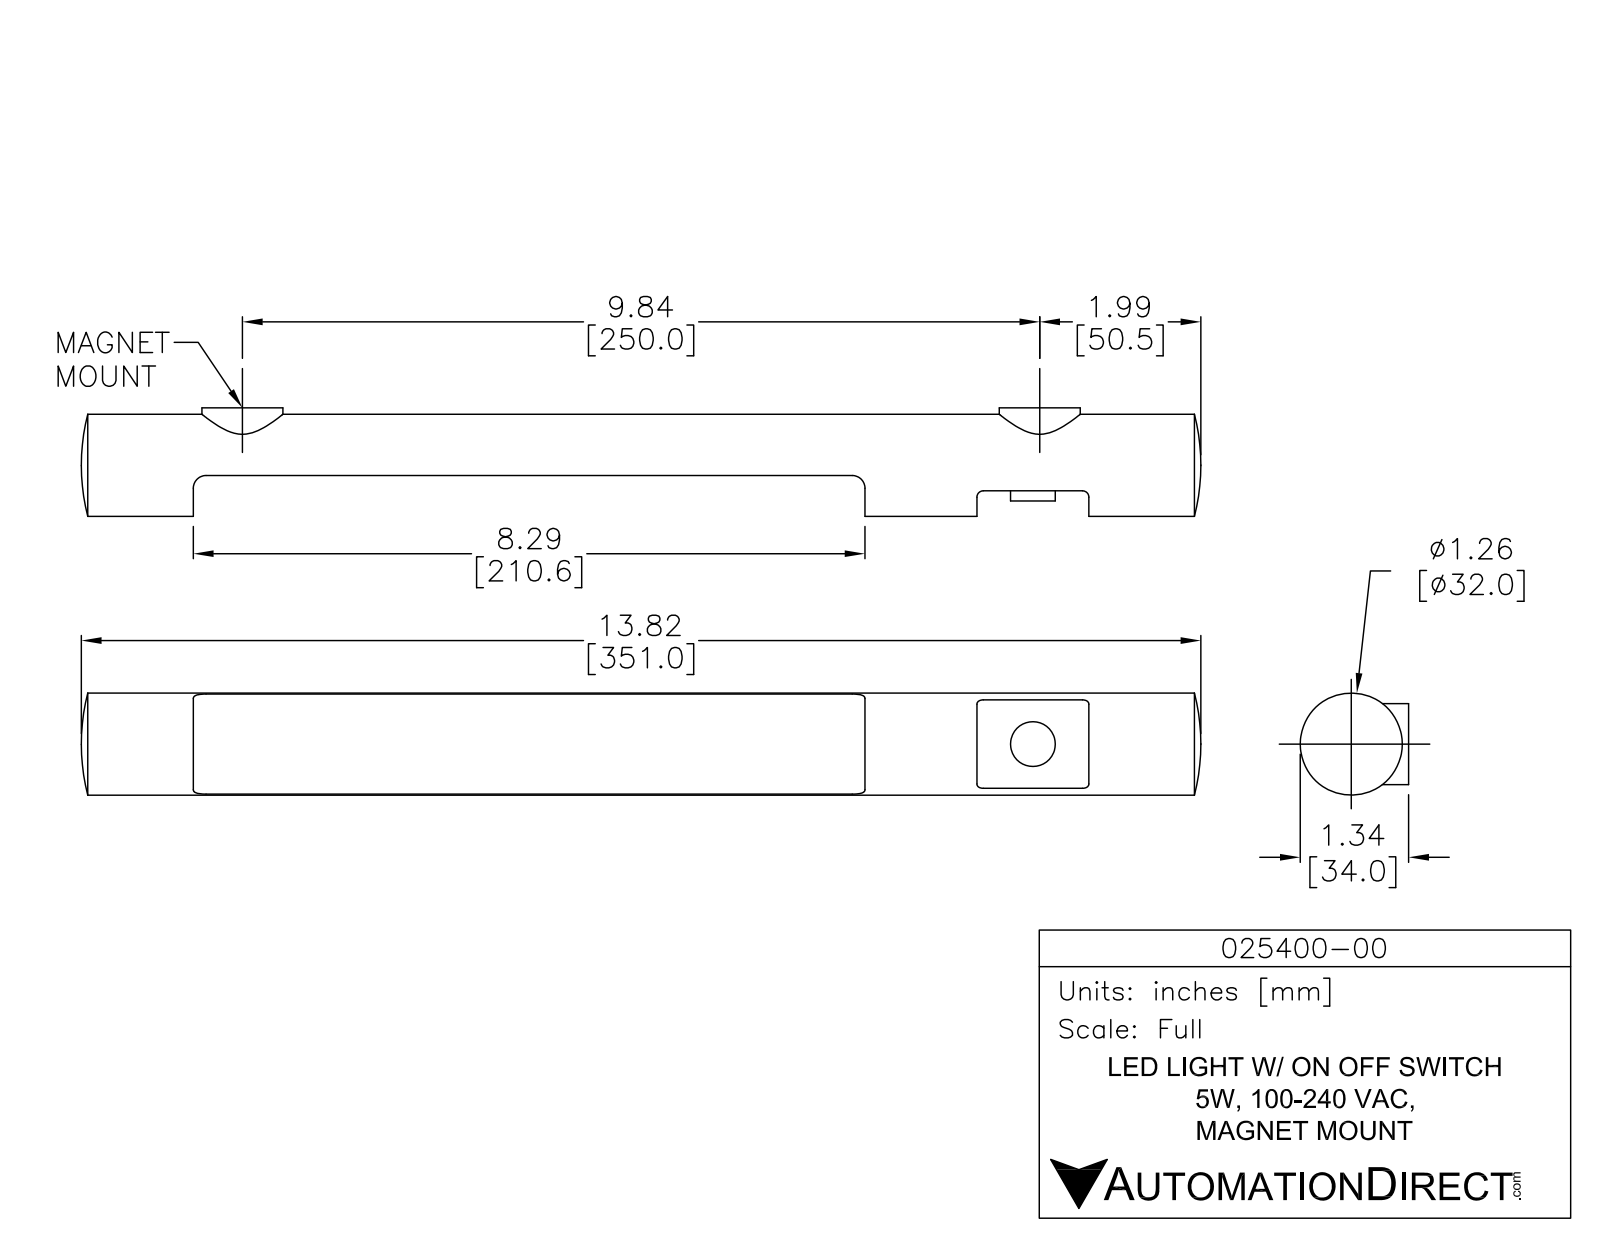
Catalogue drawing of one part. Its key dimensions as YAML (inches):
part_name: "025400-00"
step_written_by: "SolidWorks 2013 (AUTOMOTIVE_DESIGN)"
units: inches
bodies: {solids: 1, faces: 138, planar: 85, cylindrical: 33, other: 20}
overall_size: [13.758, 1.35, 1.26]
volume: 13.32
surface_area: 57.38
round_holes:
  - {diameter: 0.077, count: 2}
round_bosses_or_shafts:
  - {diameter: 0.985, count: 2}
  - {diameter: 0.073, count: 2}
  - {diameter: 1.26, count: 1}
  - {diameter: 0.865, count: 1}
  - {diameter: 0.865, count: 1}
partial_cylinders:
  - {radius: 0.06, count: 4}
  - {radius: 0.2, count: 4}
  - {radius: 0.12, count: 2}
  - {radius: 0.03, count: 1}
  - {radius: 1.209, count: 1}
face_to_face_distances: [0.885, 0.03, 0.545, 0.22, 0.325, 0.53, 0.04, 0.845, 0.56, 0.03]
hole_center_spacings: [0.2]
